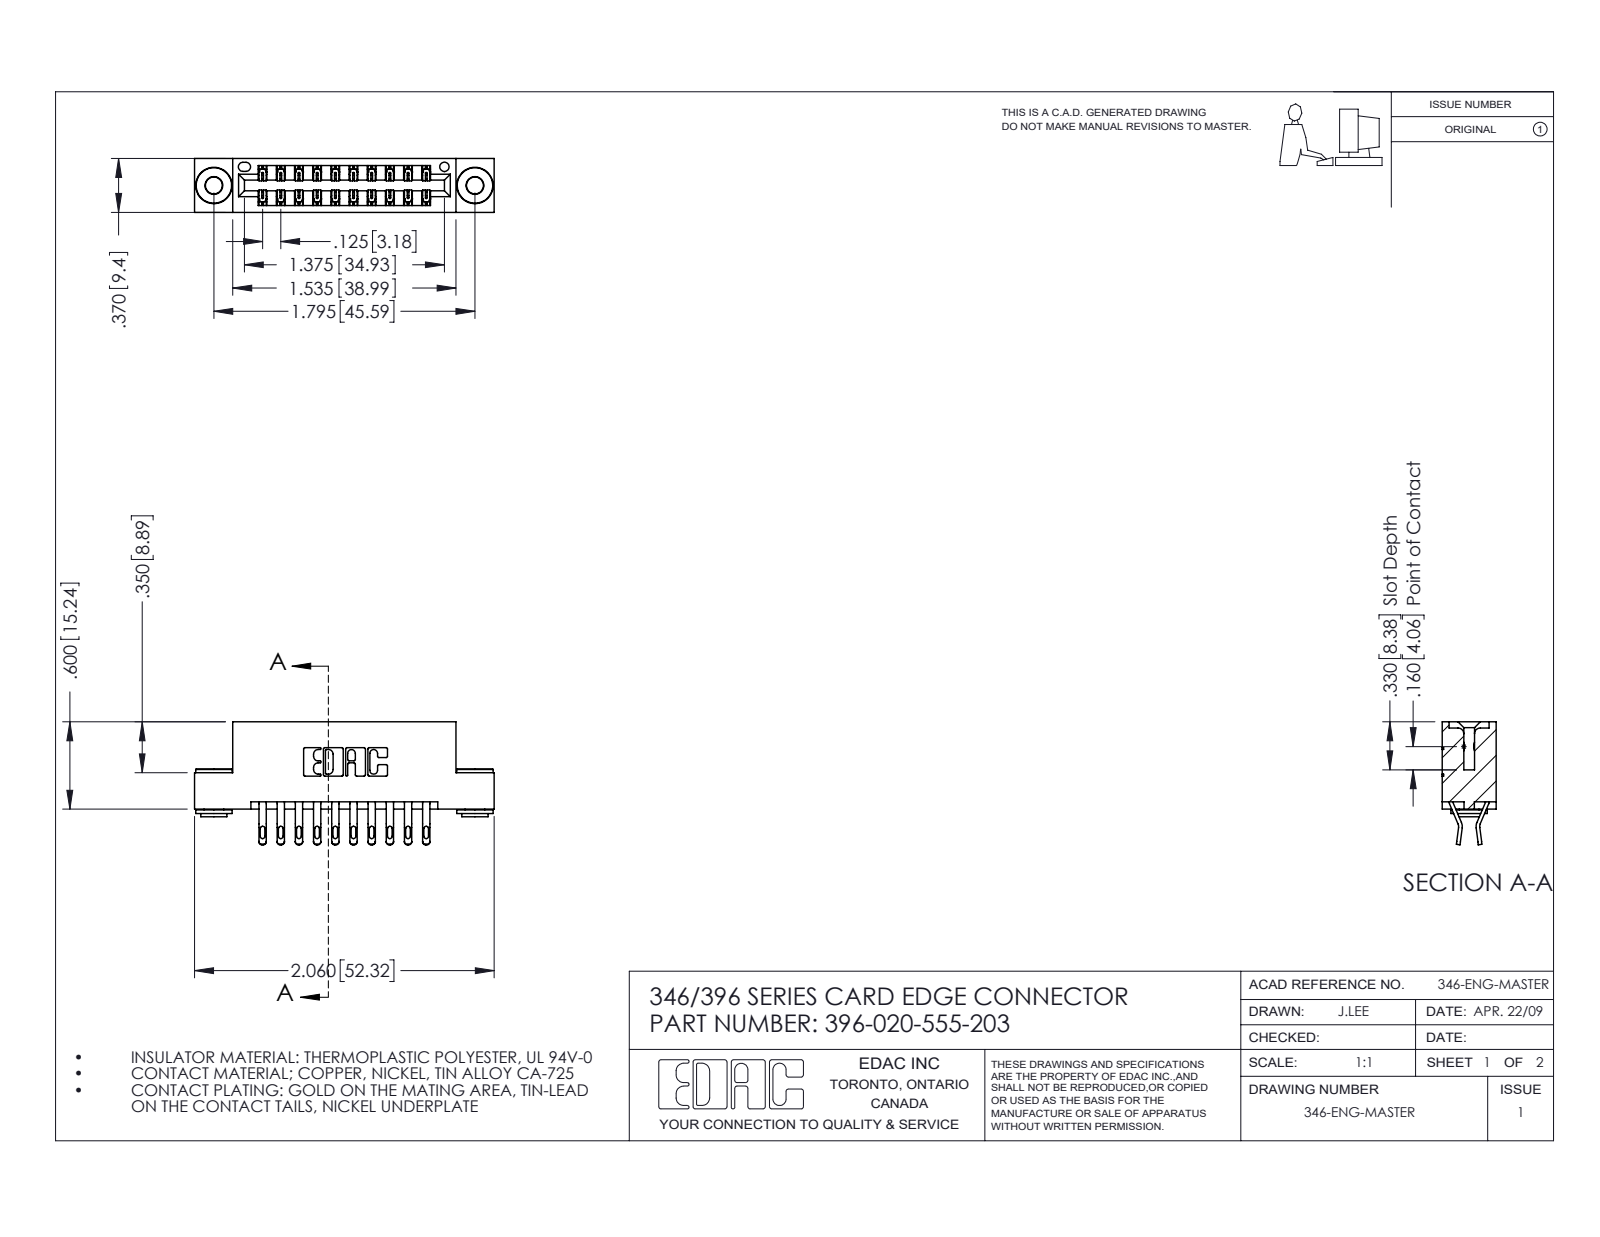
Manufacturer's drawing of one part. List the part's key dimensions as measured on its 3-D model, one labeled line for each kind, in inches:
Part name (STEP PRODUCT): 396-020-555-203; 346 Part_Flush Mounting Lugs - 0.156 Dia-TH; 345-292-001_555 Tail; 345-250-002_345-250-002-102
STEP written by: SolidWorks 2016 (CONFIG_CONTROL_DESIGN)
Units: inches
Bodies: 23 solids, 1320 faces (746 planar, 566 cylindrical, 8 other)
Overall size (bounding box): 2.06 × 0.845 × 0.37
Volume: 0.301 in³ · Surface area: 10.38 in²
Round holes (diameter × count): ⌀0.116 ×2, ⌀0.156 ×2, ⌀0.064 ×1
Round bosses / shafts (diameter × count): ⌀0.25 ×2, ⌀0.18 ×2, ⌀0.136 ×2
Partial cylindrical surfaces — rounded edges, fillets, slot ends (radius × count): R0.016 ×40, R0.02 ×40, R0.006 ×30, R0.01 ×22, R0.007 ×6, R0.031 ×6, R0.026 ×3, R0.01 ×2
Main face-to-face distances: 0.25, 0.048, 0.322, 0.37, 0.025, 0.072, 0.298, 0.148, 0.275, 0.222
Hole centre spacings: 0.246, 1.59, 1.795
